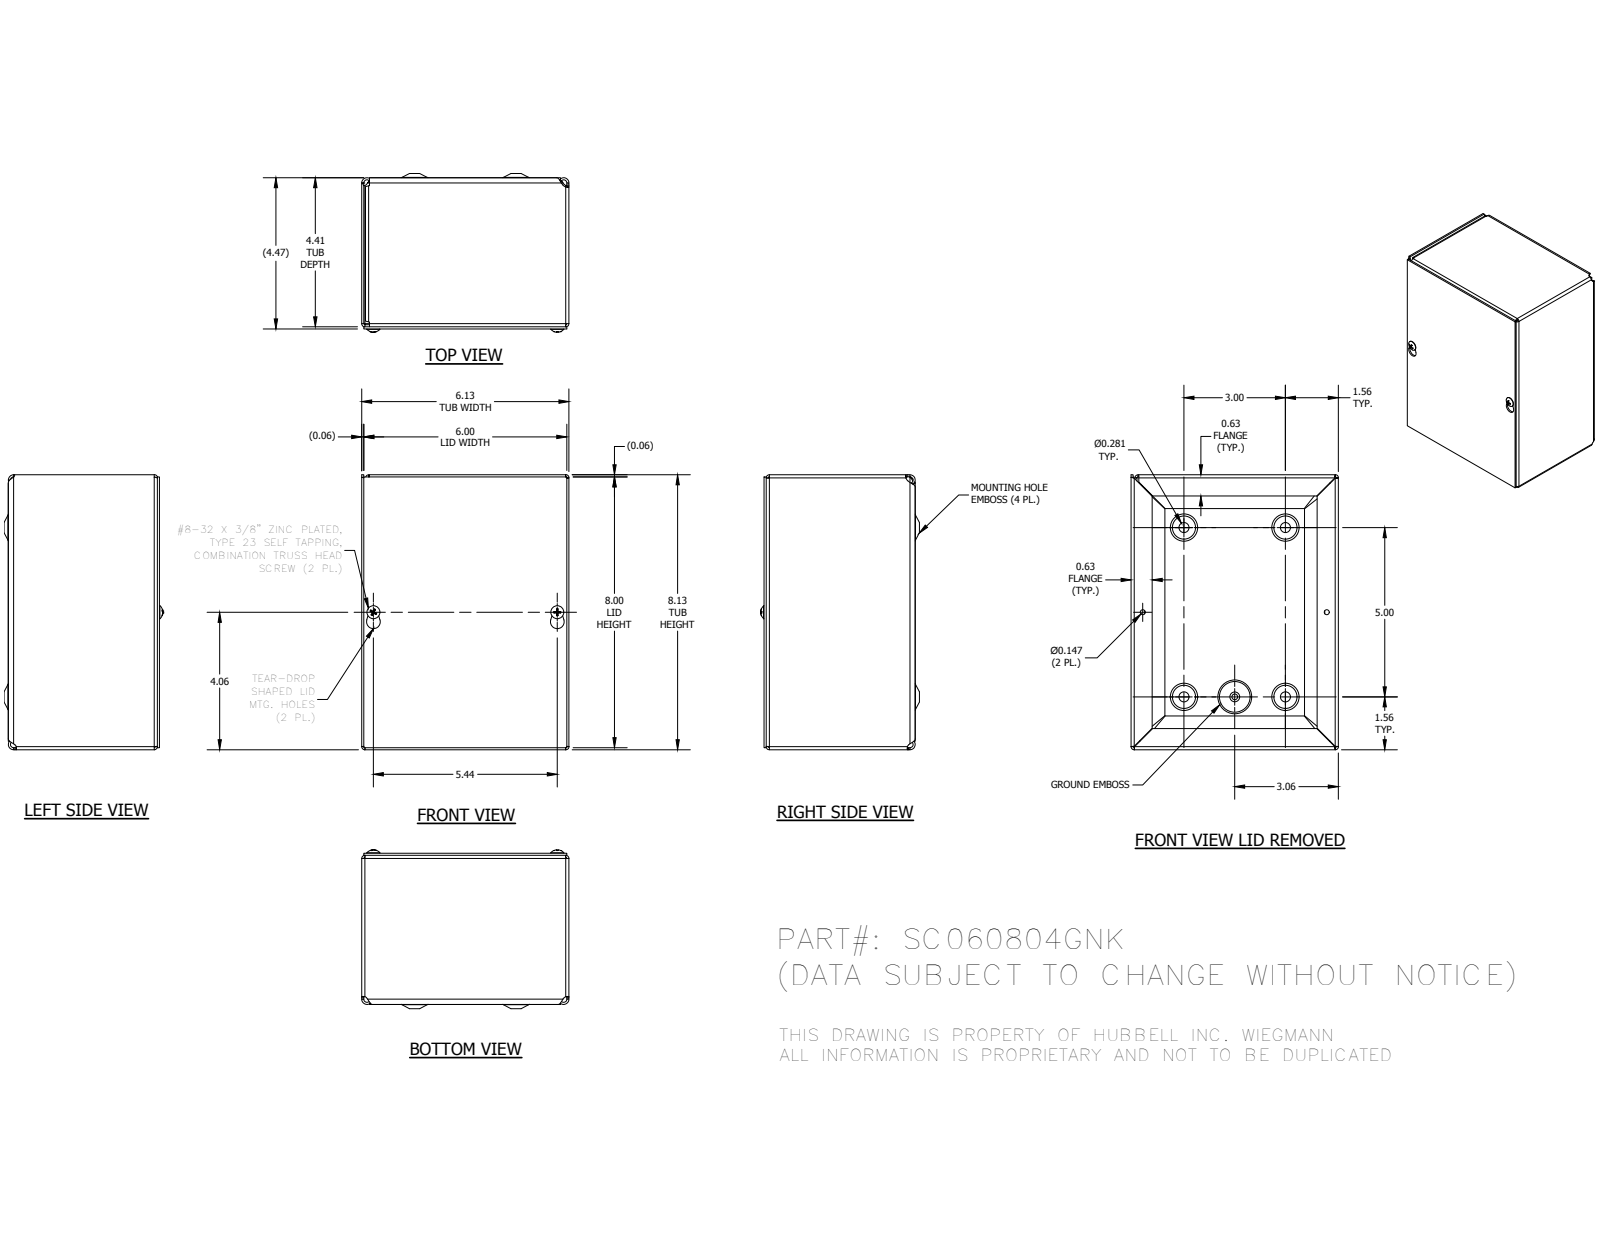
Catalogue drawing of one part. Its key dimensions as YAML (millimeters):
part_name: "SC0608GNKBKP; SC060804GNKWRA; SC0608GNKLID; 34056 (+1 more)"
step_written_by: "Autodesk Inventor 2014 (AUTOMOTIVE_DESIGN)"
units: millimeters
bodies: {solids: 5, faces: 294, planar: 109, cylindrical: 63, other: 122}
overall_size: [206.38, 155.57, 119.2]
volume: 256168
surface_area: 330752
round_holes:
  - {diameter: 7.62, count: 4}
  - {diameter: 3.73, count: 2}
  - {diameter: 4.19, count: 1}
round_bosses_or_shafts:
  - {diameter: 9.75, count: 2}
  - {diameter: 4.17, count: 2}
  - {diameter: 5.8, count: 1}
partial_cylinders:
  - {radius: 0.79, count: 8}
  - {radius: 2.37, count: 8}
  - {radius: 1.4, count: 4}
  - {radius: 1.57, count: 4}
  - {radius: 2.38, count: 4}
  - {radius: 2.97, count: 4}
  - {radius: 3.15, count: 4}
  - {radius: 3.96, count: 4}
face_to_face_distances: [1.57, 154, 110.32, 204.8, 111.89, 1.59, 111.91, 113.48, 152.43, 155.57]
hole_center_spacings: [38.1, 70.66, 76.2, 93.8, 127, 132.59, 148.11, 70.62]
